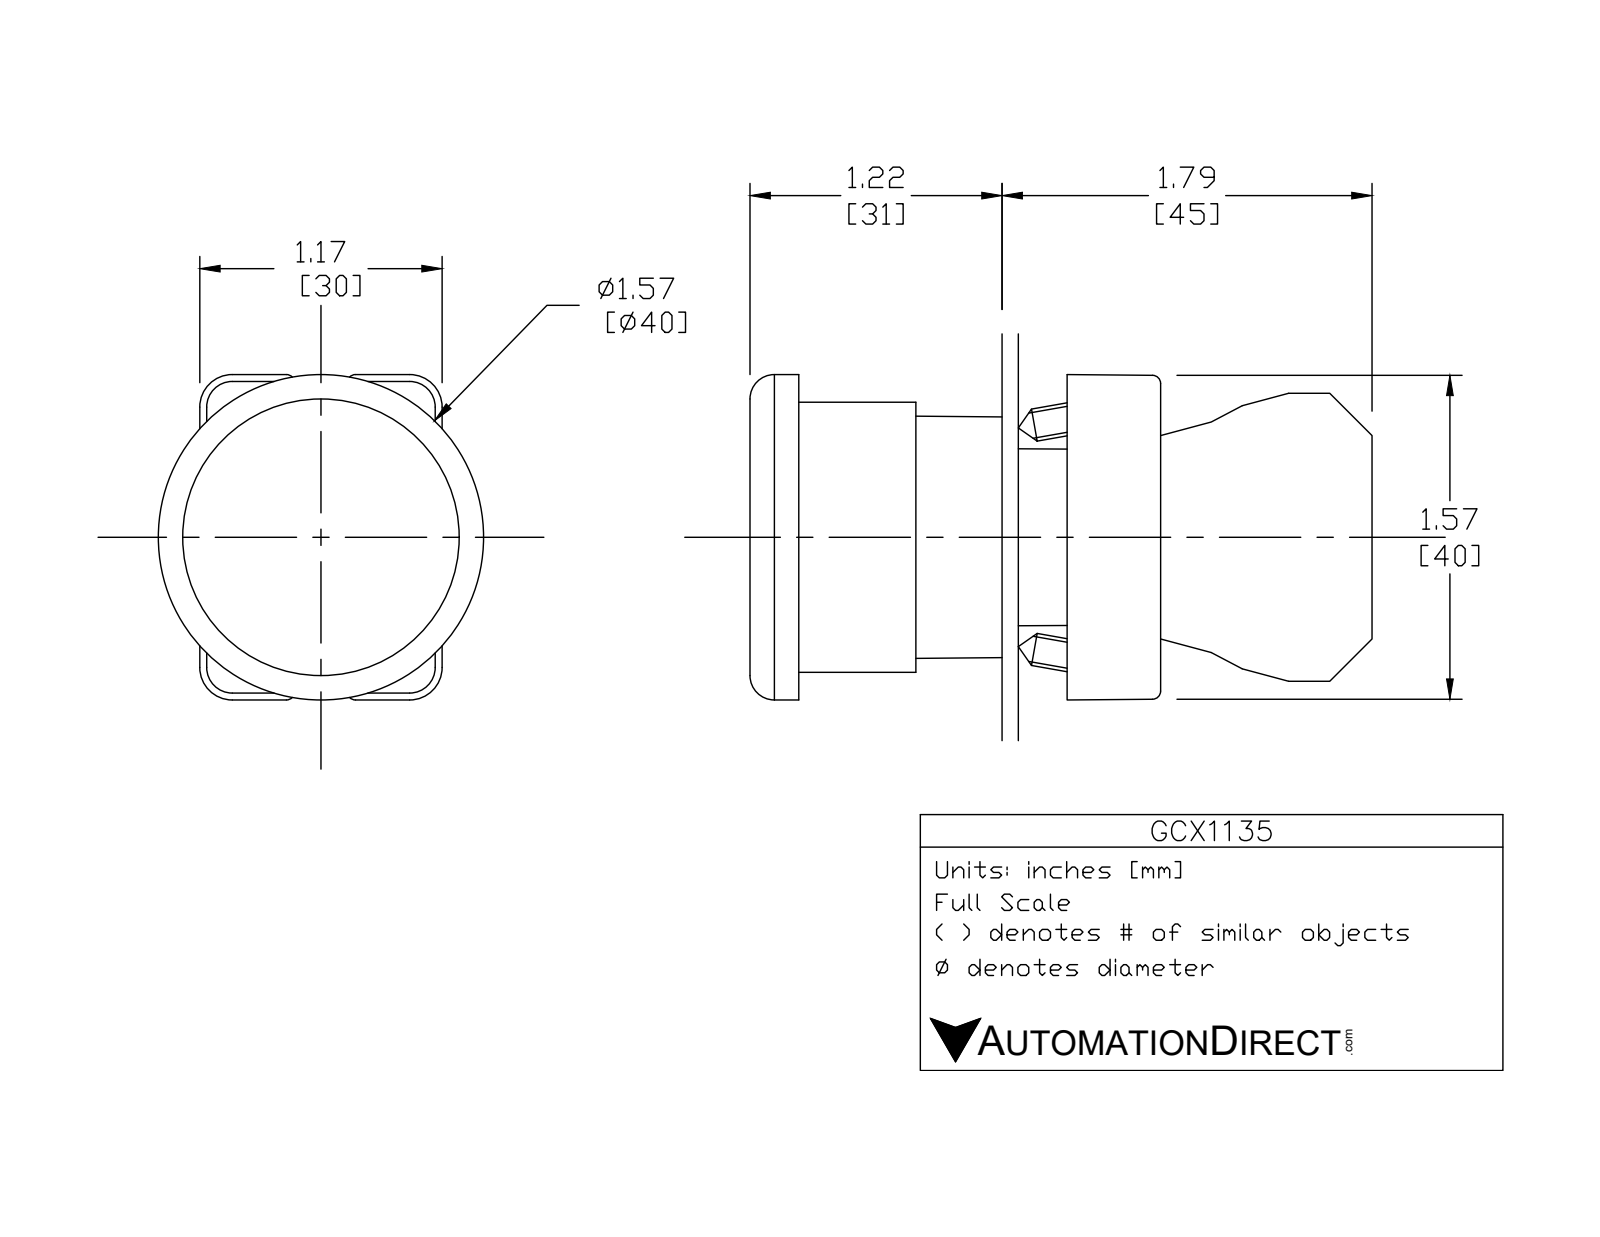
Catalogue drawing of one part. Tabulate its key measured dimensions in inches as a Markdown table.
| quantity | value |
| --- | --- |
| part name | ecx1030; GCX1135 OPERATOR; ECX1029-2; GCX1135 |
| STEP written by | SolidWorks 2016 (AUTOMOTIVE_DESIGN) |
| units | inches |
| bodies | 6 solids, 389 faces (224 planar, 136 cylindrical, 29 other) |
| overall size | 2.944 × 1.581 × 1.575 |
| volume | 1.871 in³ |
| surface area | 33.58 in² |
| round holes (diameter × count) | 0.079 × 2, 0.124 × 2, 0.13 × 2, 0.087 × 1, 0.197 × 1, 0.878 × 1, 0.888 × 1, 1.024 × 1, 1.181 × 1 |
| round bosses / shafts (diameter × count) | 0.157 × 2, 1.575 × 1, 1.299 × 1, 1.175 × 1, 0.945 × 1, 0.856 × 1, 0.78 × 1 |
| partial cylindrical surfaces (radius × count) | 0.059 × 24, 0.041 × 12, 0.124 × 12, 0.157 × 12, 0.039 × 4, 0.128 × 2, 0.02 × 1, 0.063 × 1 |
| main face-to-face distances | 1.921, 0.579, 0.033, 1.763, 0.157, 1.724, 0.031, 1.024, 0.76, 1.004 |
| hole center spacings | 0.236, 0.544, 0.472, 0.49 |
